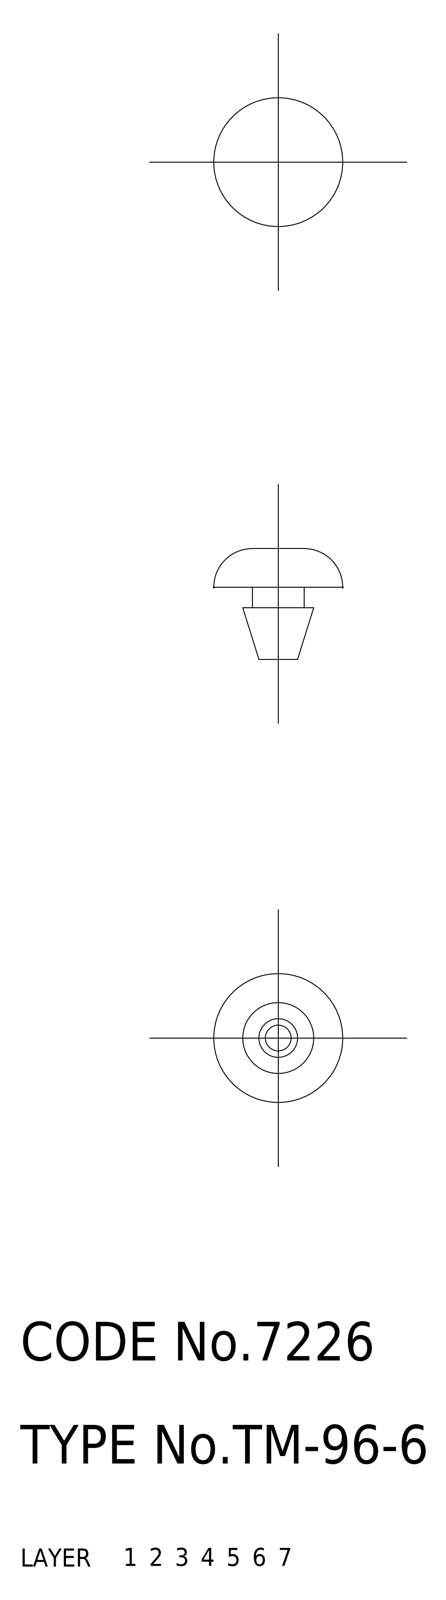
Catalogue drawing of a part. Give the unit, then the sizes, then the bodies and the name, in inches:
Units: inches
Overall size (bounding box): 0.394 × 0.394 × 0.339
Volume: 0.015 in³ · Surface area: 0.502 in²
Bodies: 1 solid, 13 faces (0 planar, 0 cylindrical, 13 other)
Part name (STEP PRODUCT): cushion
STEP written by: CADfix (AUTOMOTIVE_DESIGN)
